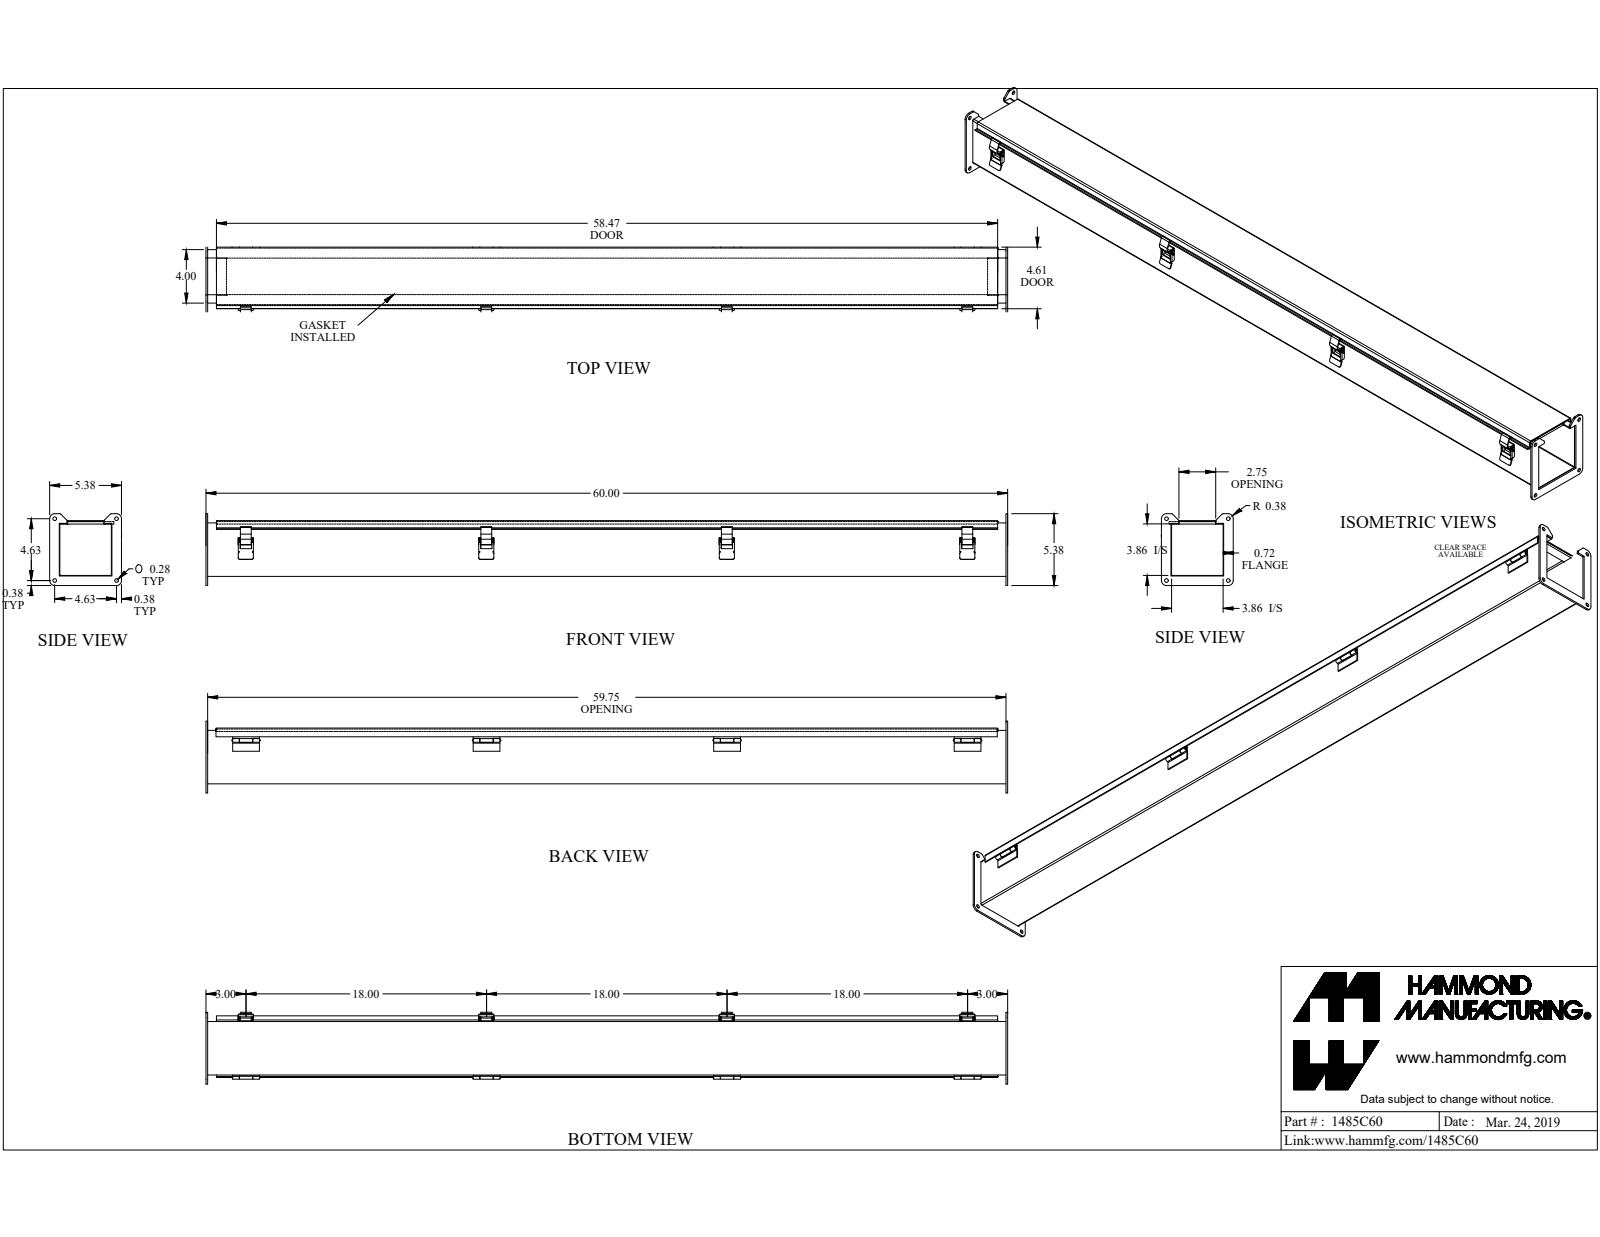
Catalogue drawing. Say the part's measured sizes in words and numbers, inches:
The part is named "1485C60". Its 3-D file was written by "SolidWorks 2019 (CONFIG_CONTROL_DESIGN)". It is 32 solids with 700 faces: 418 planar, 274 cylindrical and 8 other. Overall it measures 60 by 5.383 by 5.375 inches. Its volume is 101.3 cubic inches and its surface area 2 581 square inches. Round holes: 4 of diameter 0.281, 1 of diameter 0.125, 1 of diameter 0.13, 1 of diameter 0.164. Round bosses or shafts: 2 of diameter 0.187, 1 of diameter 0.275, 1 of diameter 0.156, 1 of diameter 0.125. Partial cylindrical surfaces (rounded edges, fillets, slot ends): 25 of radius 0.016, 13 of radius 0.125, 9 of radius 0.035, 9 of radius 0.039, 9 of radius 0.076, 8 of radius 0.015, 8 of radius 0.029, 8 of radius 0.086. The main face-to-face distances are 0.072, 3.928, 4.1, 4, 3.856, 4.172, 4.028, 0.172, 3.913, 3.841. The hole center spacings are 4.625, 6.541, 0.285, 1.075, 1.57, 1.849, 2.785, 3.057.
